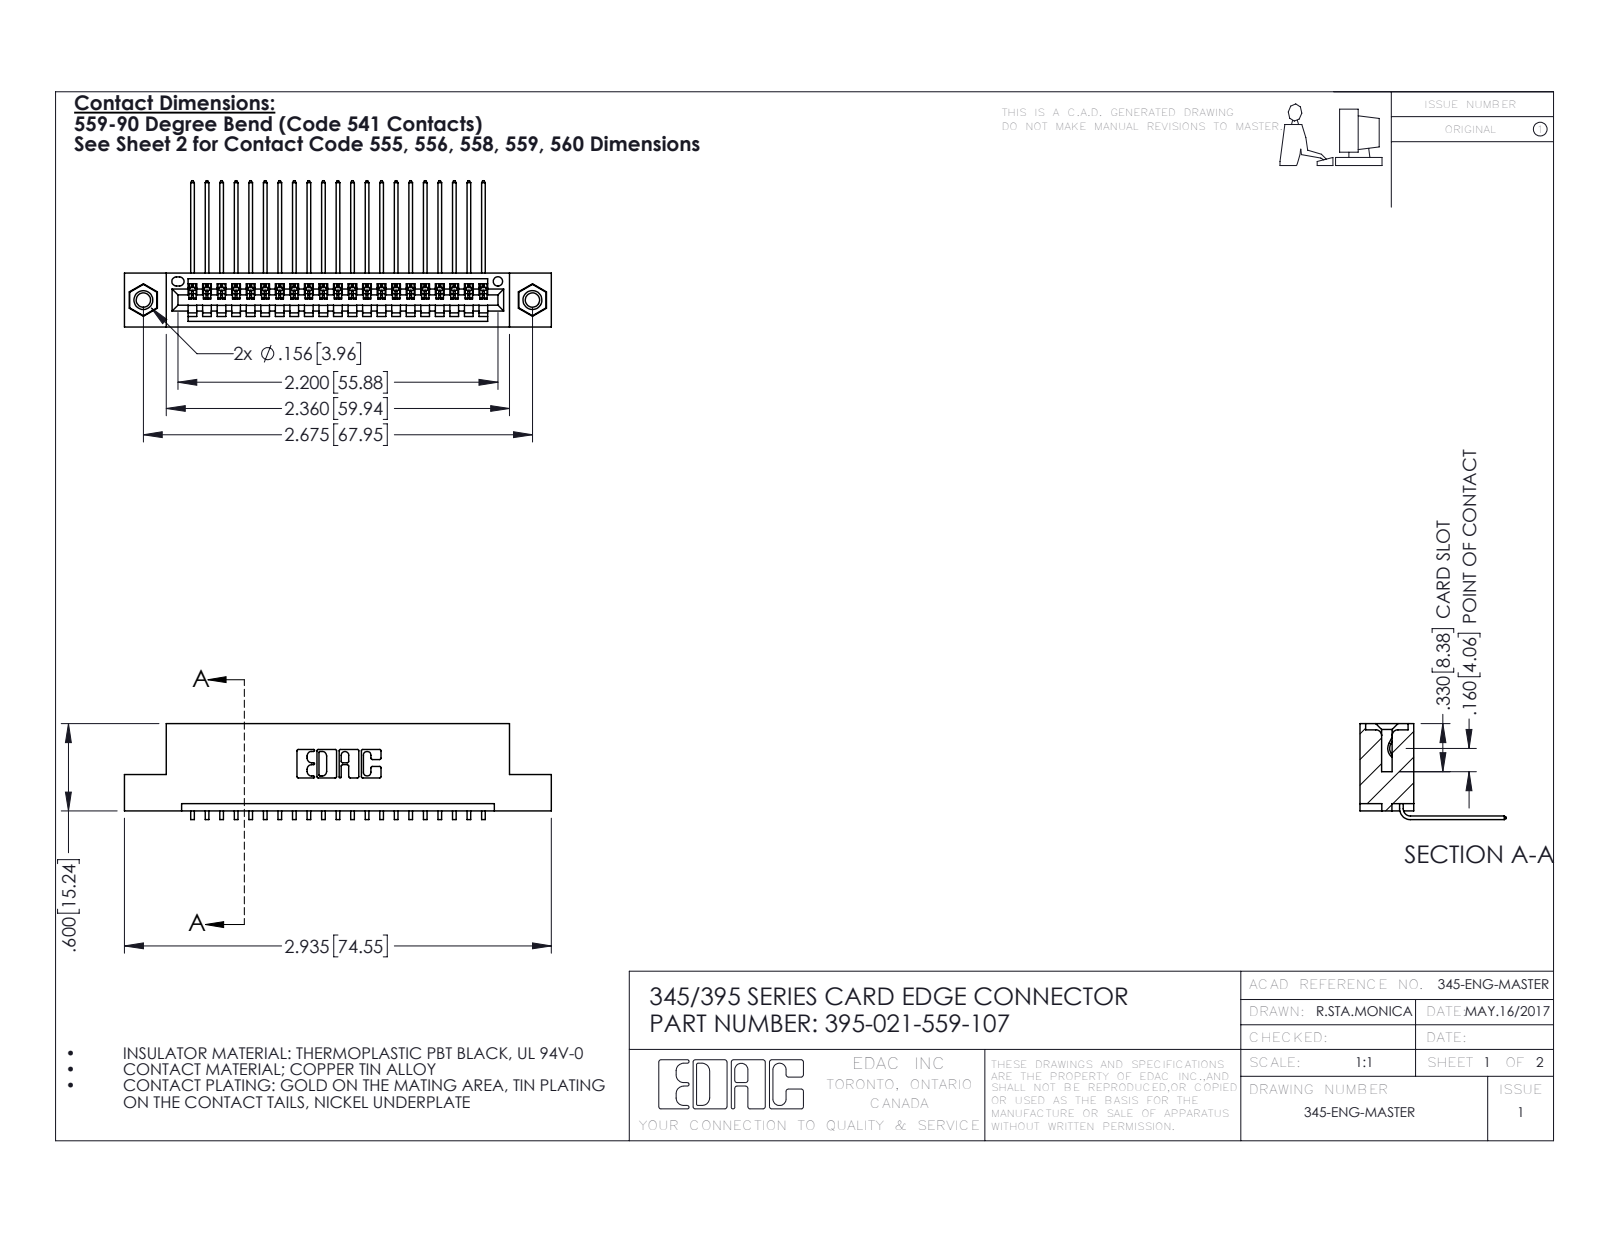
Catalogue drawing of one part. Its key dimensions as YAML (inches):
part_name: "345 Part_Flush Mounting Lugs - 0.156 Dia-TI; 345-292-001_558 559 Tail - 1; 395-021-559-107; 345-250-001_345-250-005-103"
step_written_by: "SolidWorks 2016 (CONFIG_CONTROL_DESIGN)"
units: inches
bodies: {solids: 24, faces: 1446, planar: 994, cylindrical: 436, other: 16}
overall_size: [2.935, 1.005, 0.659]
volume: 0.425
surface_area: 14.59
round_holes:
  - {diameter: 0.098, count: 2}
  - {diameter: 0.125, count: 2}
  - {diameter: 0.156, count: 2}
  - {diameter: 0.064, count: 1}
round_bosses_or_shafts:
  - {diameter: 0.155, count: 2}
partial_cylinders:
  - {radius: 0.006, count: 42}
  - {radius: 0.01, count: 22}
  - {radius: 0.007, count: 6}
  - {radius: 0.031, count: 6}
  - {radius: 0.026, count: 3}
  - {radius: 0.031, count: 2}
  - {radius: 0.04, count: 2}
  - {radius: 0.014, count: 1}
face_to_face_distances: [0.072, 0.298, 0.2, 0.37, 0.098, 0.272, 0.025, 0.225, 0.149, 0.072]
hole_center_spacings: [0.27, 2.441, 2.675]
